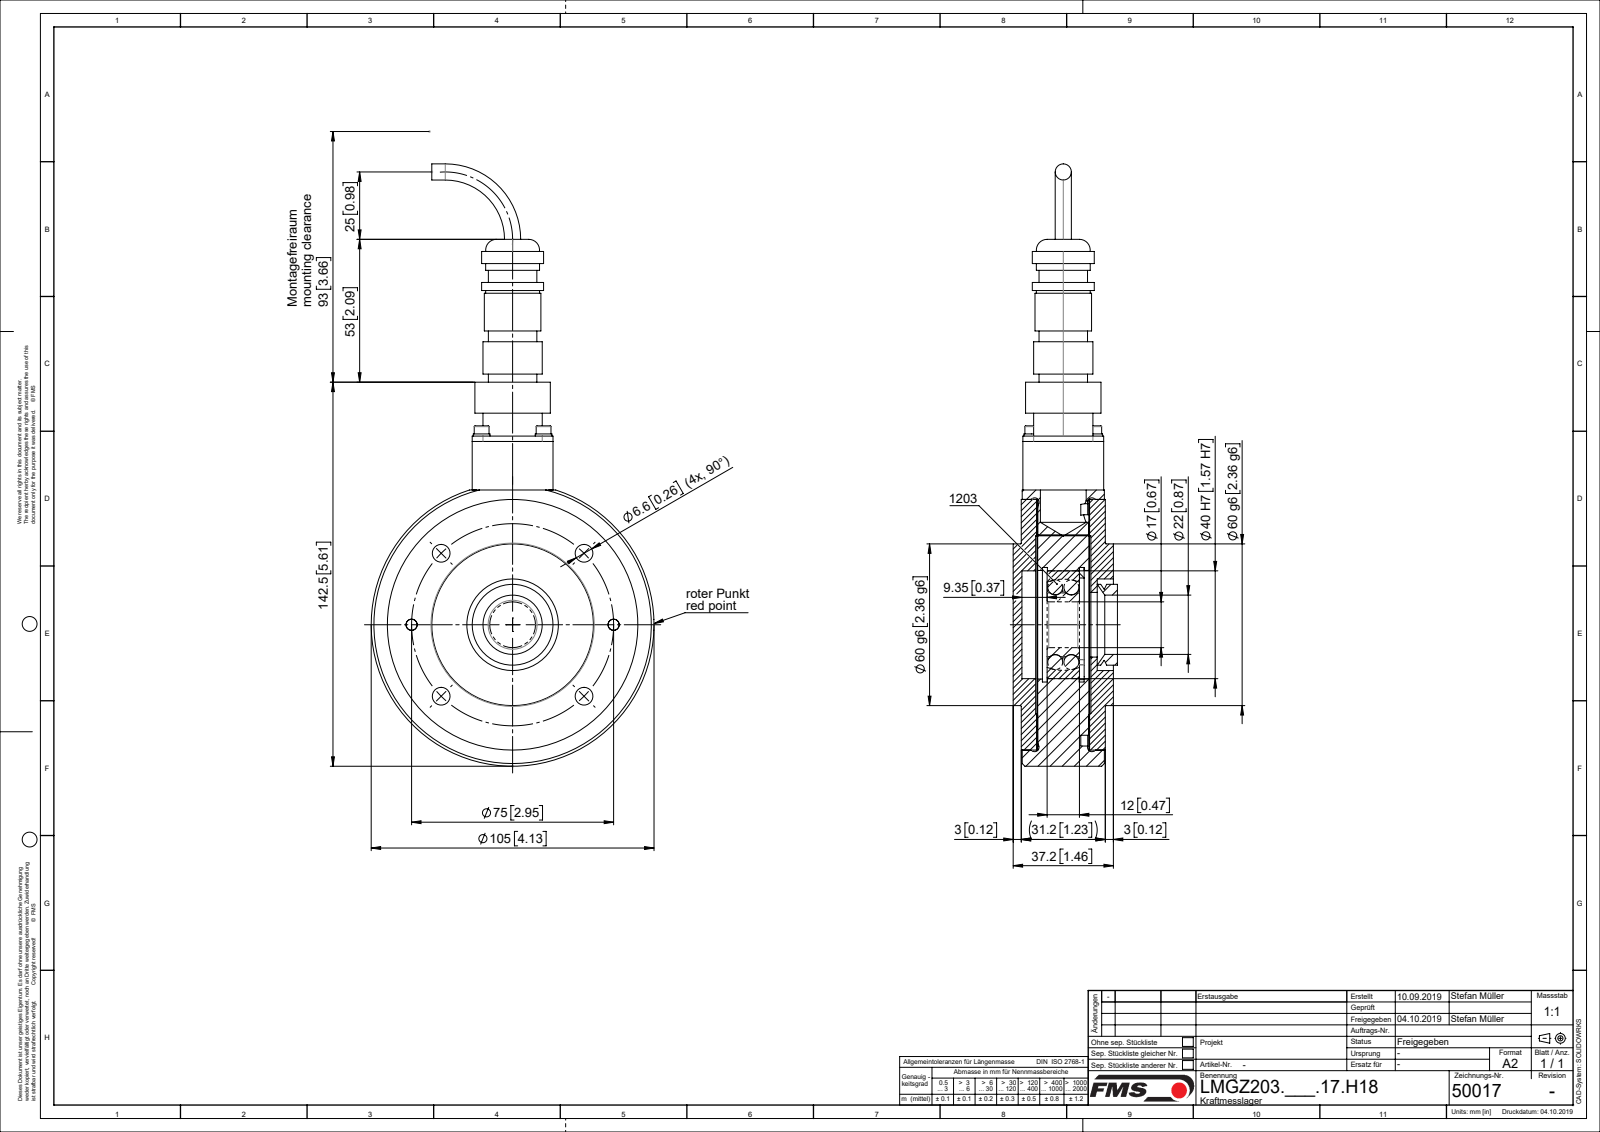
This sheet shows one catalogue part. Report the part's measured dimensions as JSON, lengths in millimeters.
{"part_name": "ZEICHNUNG4; L50017; L4795904; L47958(1) (+8 more)", "step_written_by": "Mechanical Desktop 2007 (CONFIG_CONTROL_DESIGN)", "units": "millimeters", "bodies": {"solids": 20, "faces": 372, "planar": 101, "cylindrical": 225, "other": 46}, "overall_size": [223.5, 105, 37.2], "volume_mm3": 294291, "surface_area_mm2": 104712, "round_holes": [[2.6, 4], [3.2, 4], [3.4, 4], [6.6, 4], [4, 2], [5.3, 2], [5.5, 2], [10, 2], [17, 1], [22, 1], [24, 1], [27.8, 1]], "round_bosses_or_shafts": [[6.2, 4], [5.5, 4], [3, 4], [2.5, 4], [8, 2], [5, 2], [105, 1], [93, 1]], "partial_cylinders_radius": [[4, 4], [2, 1]], "face_to_face_distances": [19.25, 5.85, 25.1, 19, 6.1, 25.35, 19.5, 20, 3, 19.75], "hole_center_spacings": [37.5, 23, 28.7, 53.04, 69.3, 32.53, 75.01, 75]}
